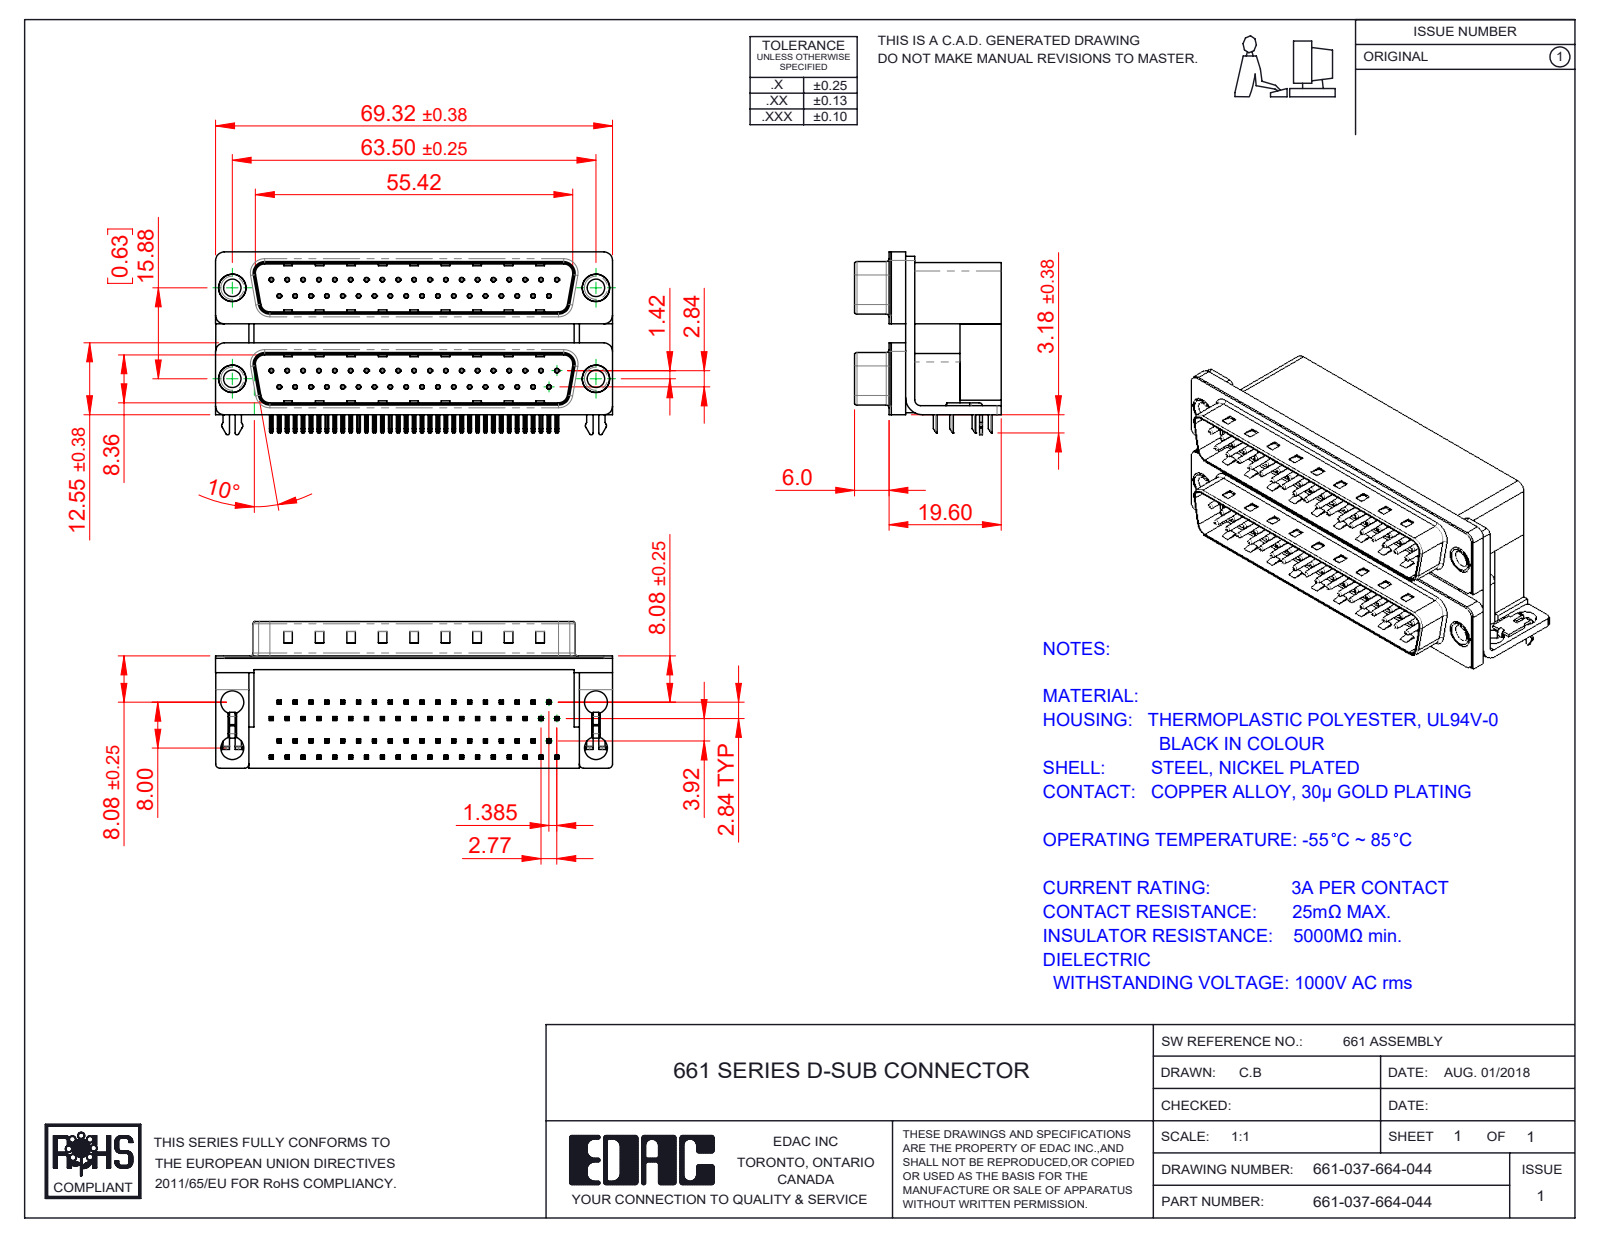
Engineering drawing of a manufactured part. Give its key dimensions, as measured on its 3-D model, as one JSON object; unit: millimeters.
{"part_name": "661 Housing Spacer_37 Contacts L; 661 Contact Bottom Upper_L; 661-037-664-044; 661 Mounting Bracket_2ProngL (+8 more)", "step_written_by": "SolidWorks 2020 (CONFIG_CONTROL_DESIGN)", "units": "millimeters", "bodies": {"solids": 87, "faces": 6606, "planar": 4328, "cylindrical": 1788, "other": 490}, "overall_size": [69.32, 31.93, 25.6], "volume_mm3": 27902, "surface_area_mm2": 28670, "round_holes": [[0.35, 74], [0.8, 74], [4, 8], [3.05, 4], [3.5, 4], [4.8, 4], [5, 4]], "round_bosses_or_shafts": [[0.75, 74], [4.9, 4], [4.75, 4], [3.85, 4]], "partial_cylinders_radius": [[0.25, 302], [0.12, 148], [0.5, 20], [1.5, 13], [0.75, 10], [0.9, 8], [1.6, 8], [2, 8]], "face_to_face_distances": [0.4, 19.2, 15.87, 7.2, 12, 10.7, 8.76, 15.52, 26.22, 2.19], "hole_center_spacings": [2.77, 5.54, 3.16, 8.31, 11.08, 13.85, 16.62, 19.39]}
